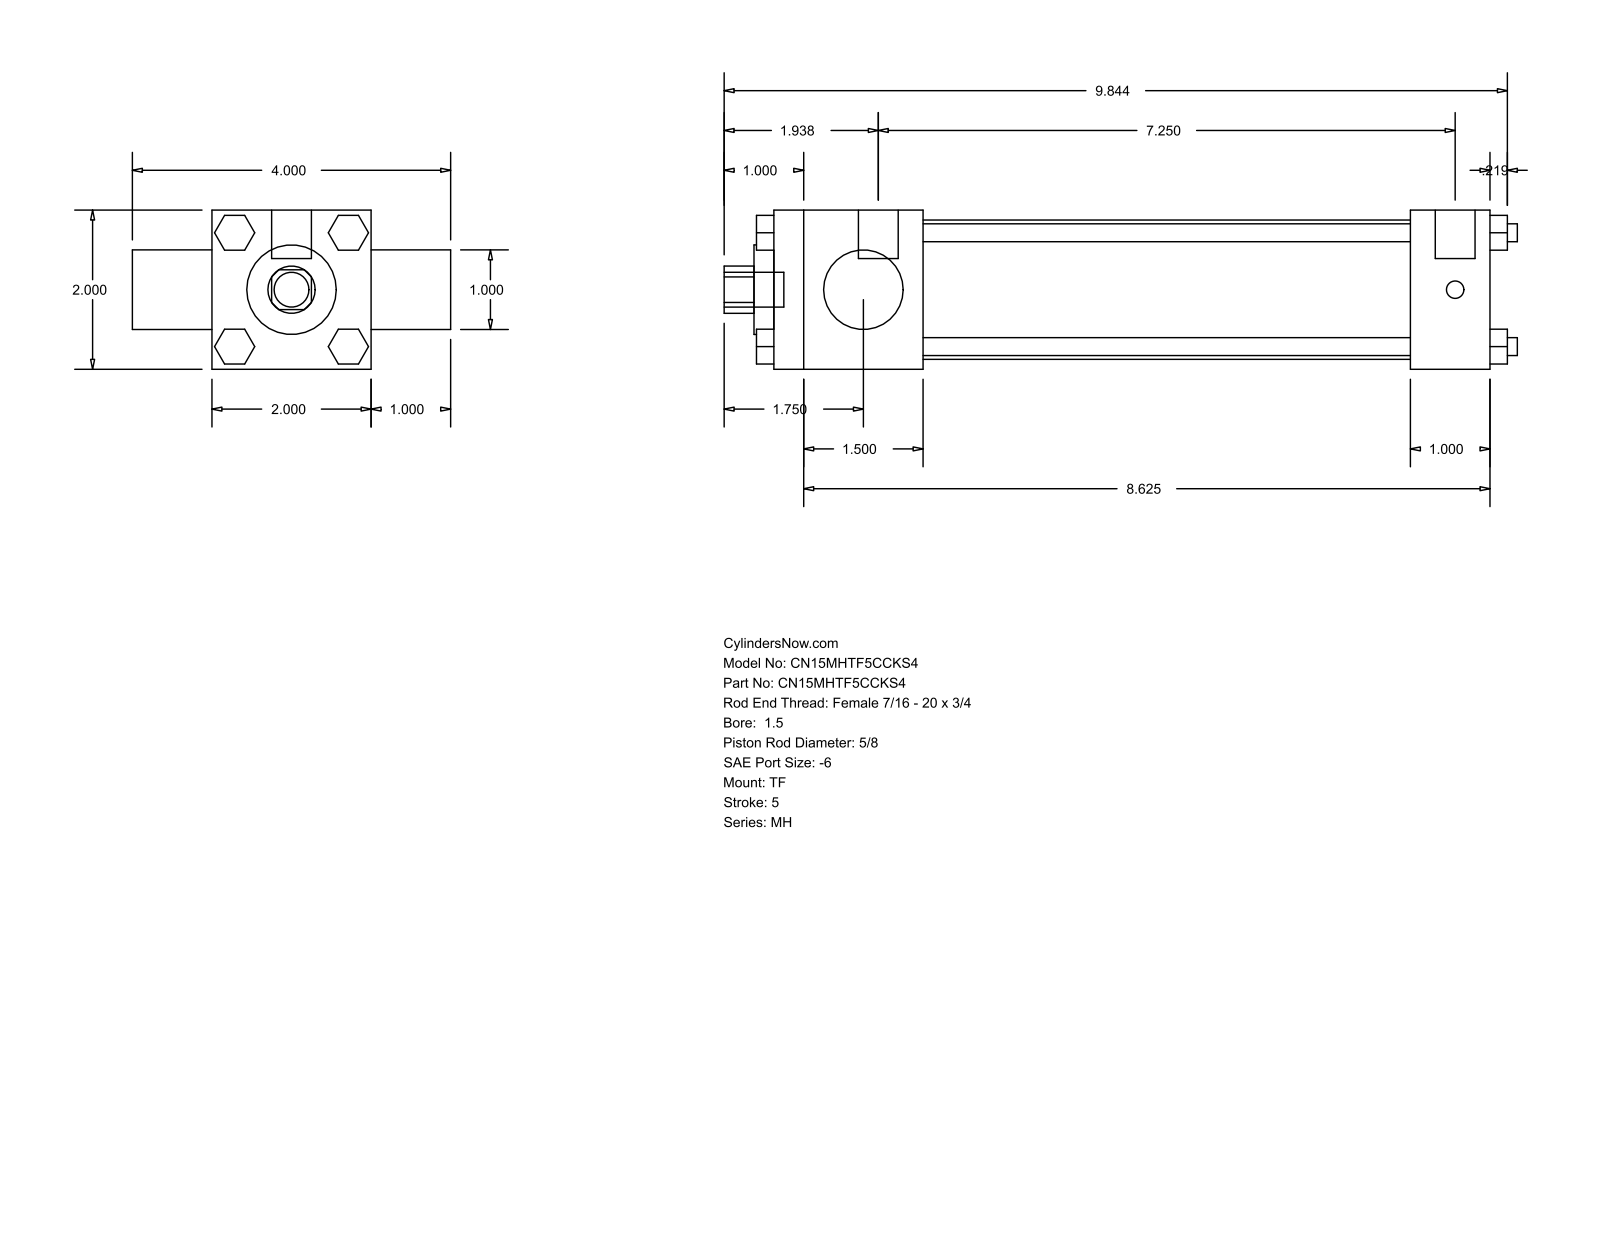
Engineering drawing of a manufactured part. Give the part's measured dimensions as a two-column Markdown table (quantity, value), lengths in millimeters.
| quantity | value |
| --- | --- |
| part name | MH_TF__0150_0.625 |
| STEP written by | GSSL Pune (CONFIG_CONTROL_DESIGN) |
| units | millimeters |
| bodies | 0 solids, 120 faces (92 planar, 28 cylindrical, 0 other) |
| overall size | 253.21 × 101.6 × 50.8 |
| round holes (diameter × count) | 15.88 × 1, 25.4 × 1, 28.57 × 1, 44.45 × 1 |
| round bosses / shafts (diameter × count) | 5.71 × 4, 5.56 × 3, 12.7 × 2, 11.11 × 1 |
| partial cylindrical surfaces (radius × count) | 7.54 × 1 |
| main face-to-face distances | 50.8, 25.4, 228.59, 76.2, 47.62, 180.97, 203.19, 155.57, 5.56, 234.15 |
